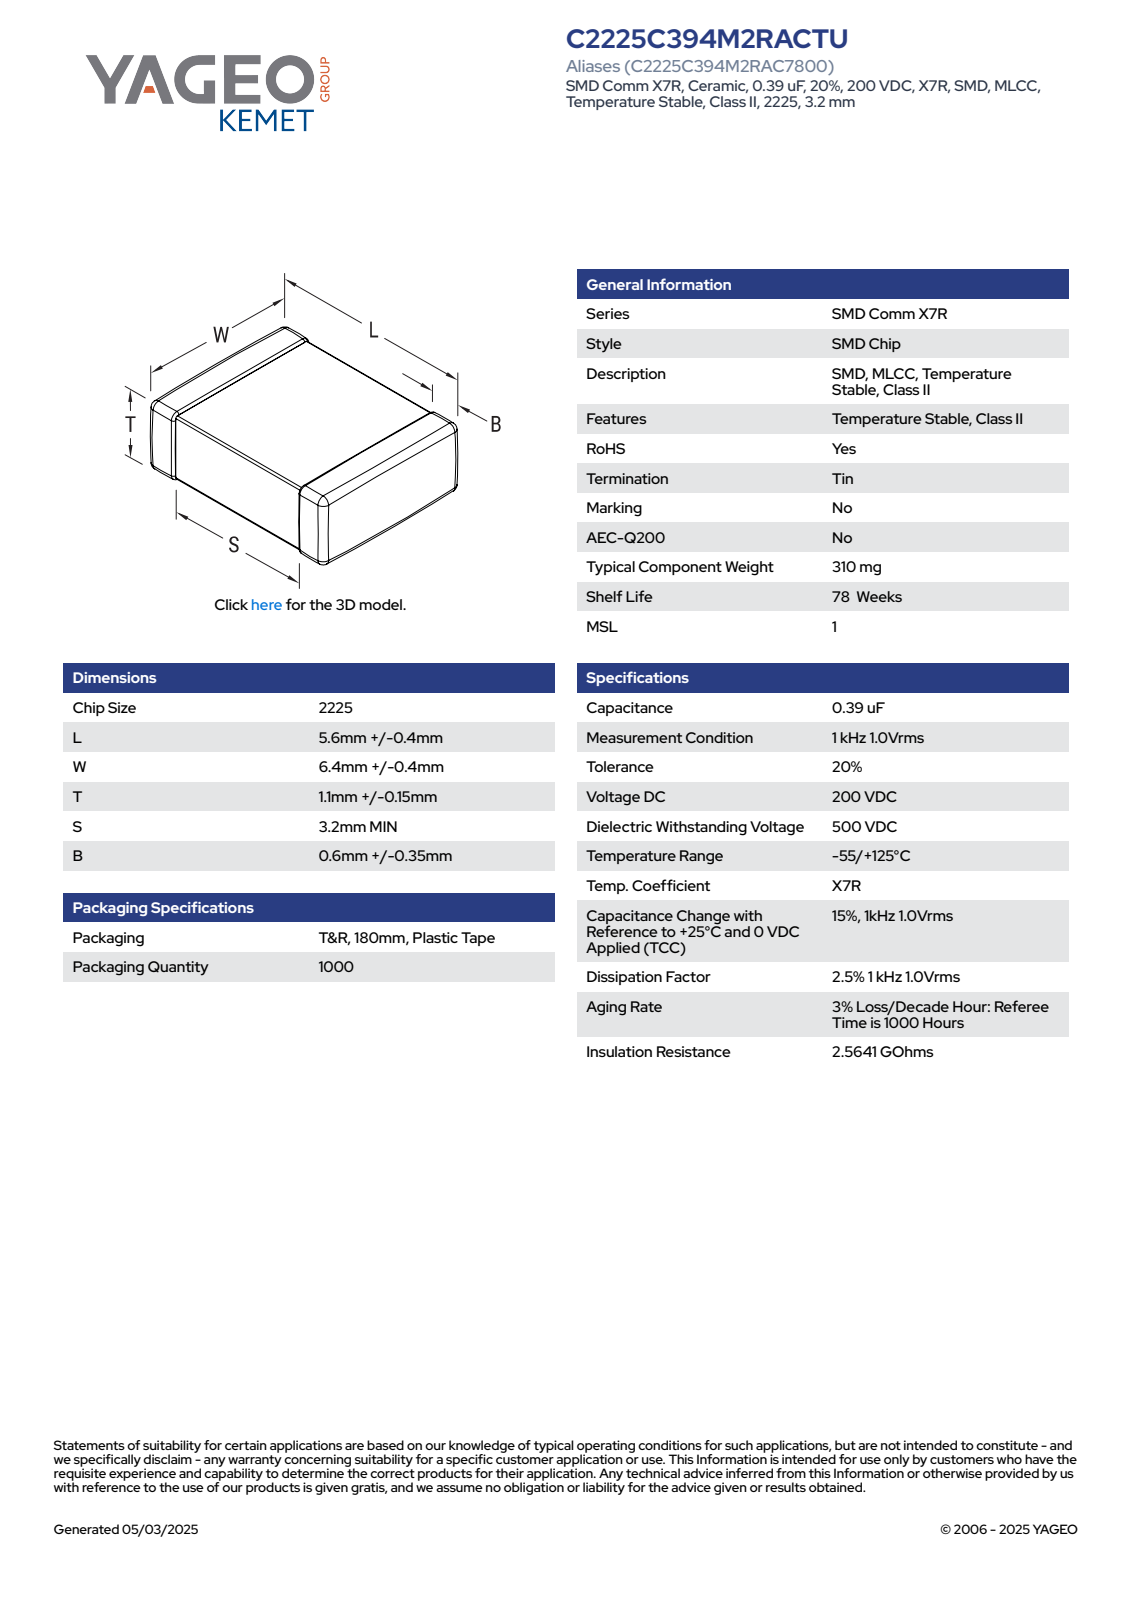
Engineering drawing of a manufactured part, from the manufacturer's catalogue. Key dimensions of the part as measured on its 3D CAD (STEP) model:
Part name (STEP PRODUCT): CCS_CCSTD_2225_L6W6.8T1.25B0.6
STEP written by: SolidWorks 2021 (AUTOMOTIVE_DESIGN)
Units: millimetres
Bodies: 4 solids, 125 faces (71 planar, 38 cylindrical, 16 other)
Overall size (bounding box): 6.8 × 6 × 1.25
Volume: 42 mm³ · Surface area: 114 mm²
Partial cylindrical surfaces — rounded edges, fillets, slot ends (radius × count): R0.14 ×24
Main face-to-face distances: 0.97, 1.11, 1.25, 6, 6.52, 6.66, 6.8, 1, 2.24, 3.76
